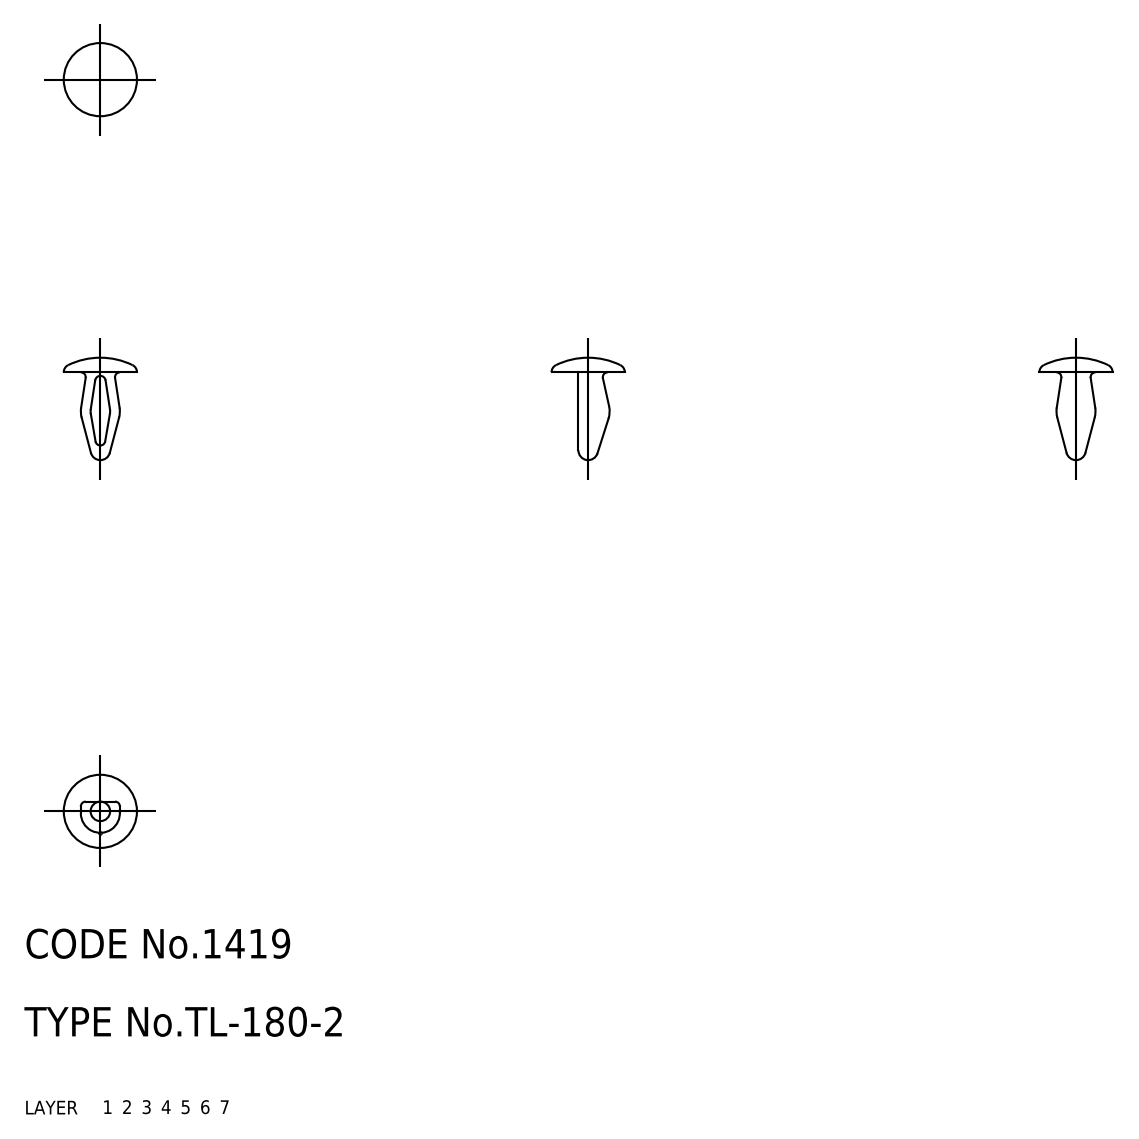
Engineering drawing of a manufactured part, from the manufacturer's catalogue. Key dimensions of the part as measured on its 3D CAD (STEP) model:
Part name (STEP PRODUCT): fastener
STEP written by: CADfix (AUTOMOTIVE_DESIGN)
Units: millimetres
Bodies: 1 solid, 26 faces (0 planar, 0 cylindrical, 26 other)
Overall size (bounding box): 10.5 × 7.5 × 7.5
Volume: 92 mm³ · Surface area: 208 mm²
